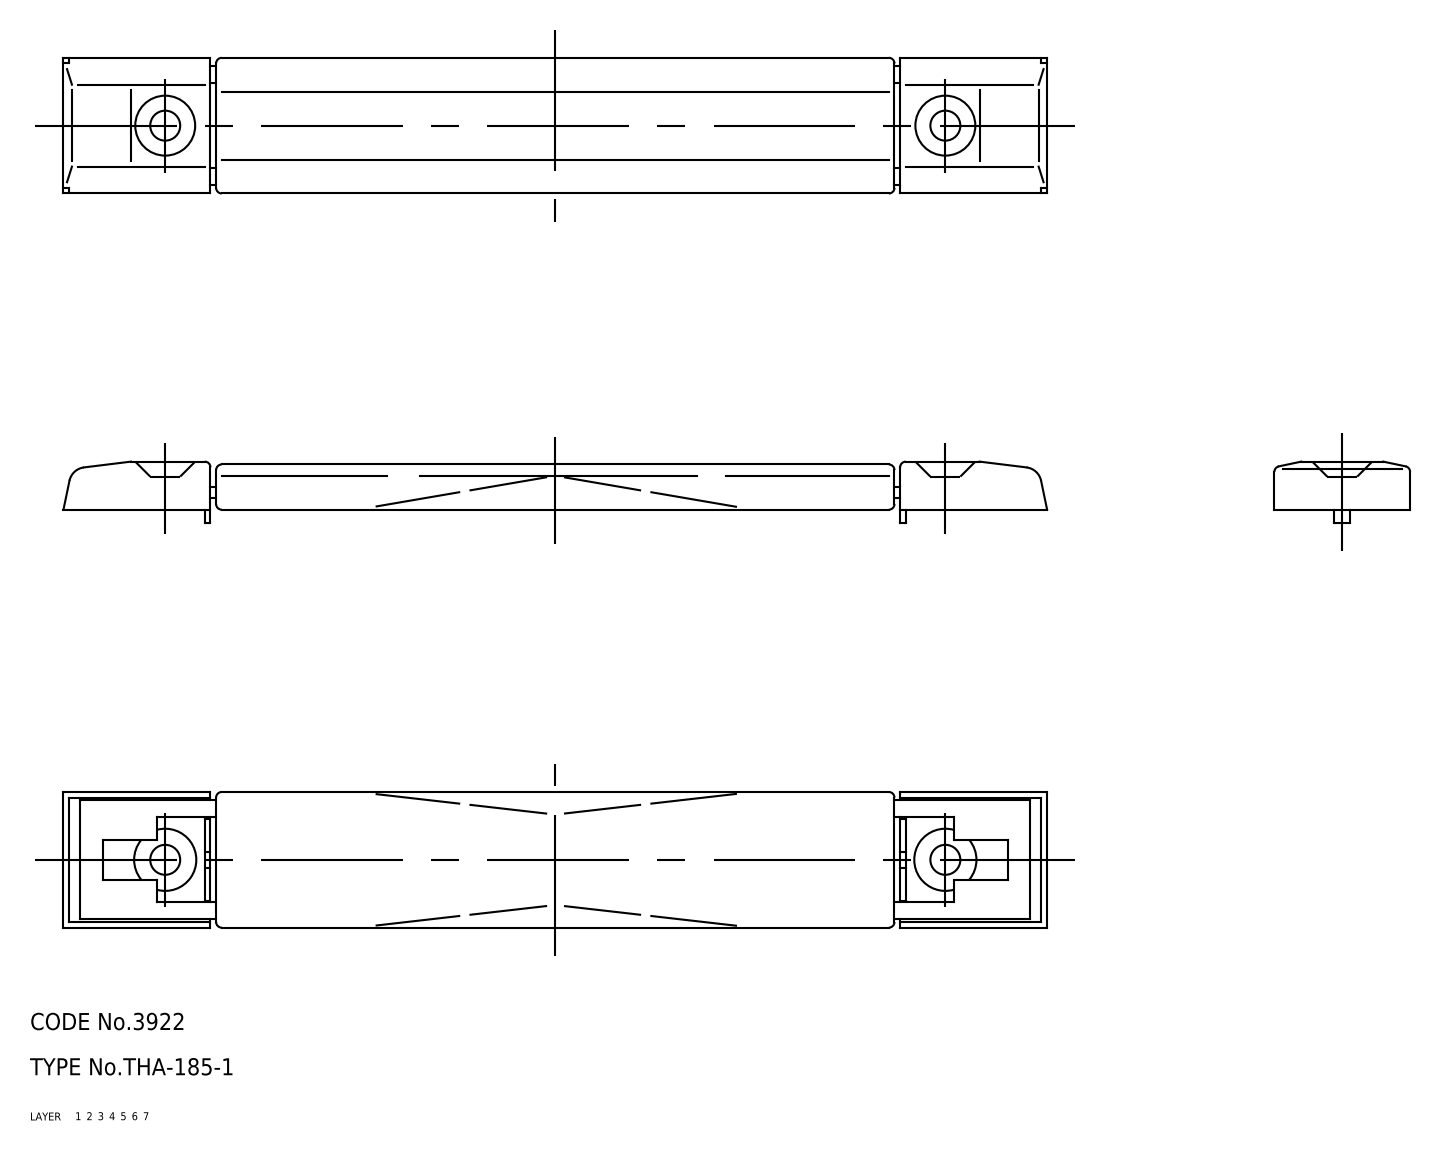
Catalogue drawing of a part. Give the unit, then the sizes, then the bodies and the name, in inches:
Units: inches
Overall size (bounding box): 6.85 × 0.945 × 0.425
Volume: 1.414 in³ · Surface area: 27.51 in²
Bodies: 5 solids, 170 faces (0 planar, 0 cylindrical, 170 other)
Part name (STEP PRODUCT): arm; bracket; grip; THA_185_1_1060_36
STEP written by: CADfix (AUTOMOTIVE_DESIGN)
